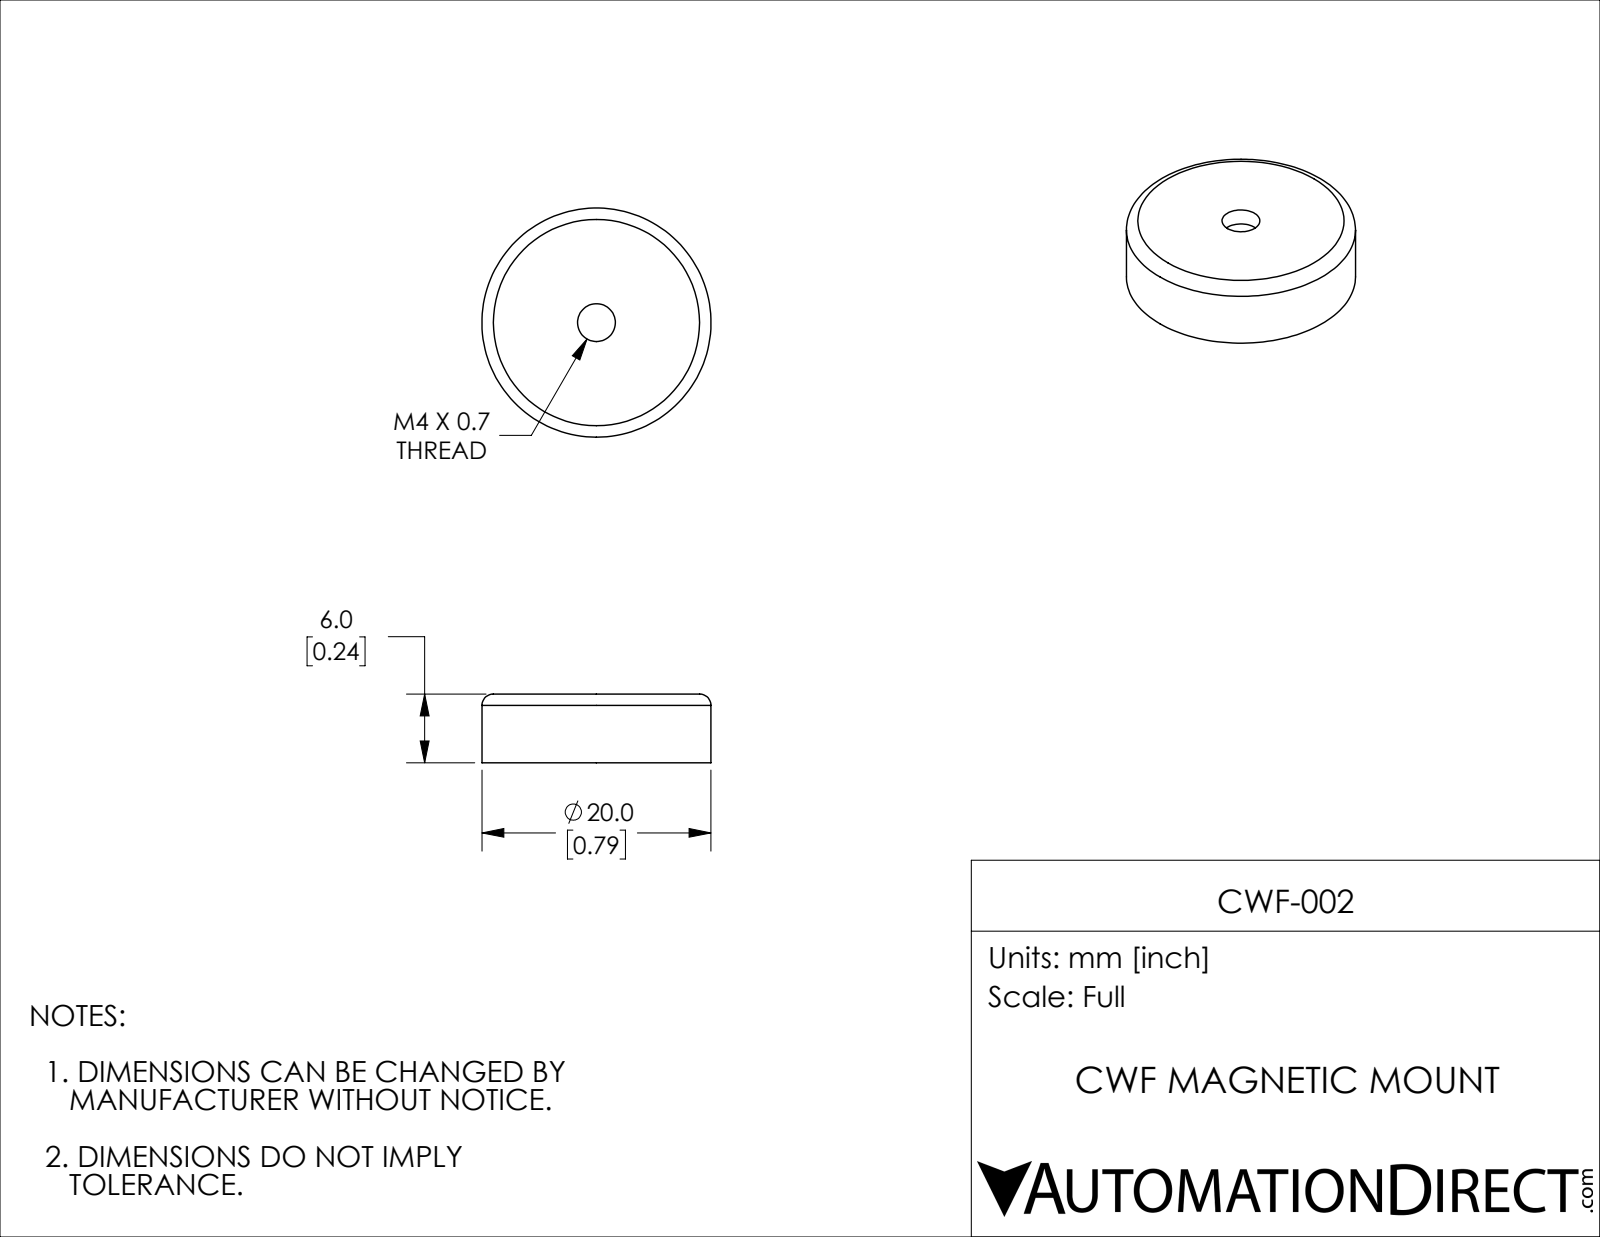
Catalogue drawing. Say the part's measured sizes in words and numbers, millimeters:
The part is named "CWF-002". Its 3-D file was written by "SolidWorks 2018 (AUTOMOTIVE_DESIGN)". It is 1 solid with 17 faces: 5 planar, 10 cylindrical and 2 other. Overall it measures 20 by 20 by 6 millimeters. Its volume is 1 500 cubic millimeters and its surface area 1 555 square millimeters. Round holes: 1 of diameter 3.3, 1 of diameter 8, 1 of diameter 17. Round bosses or shafts: 1 of diameter 20, 1 of diameter 16. The main face-to-face distances are 6, 4.5, 1.5.
